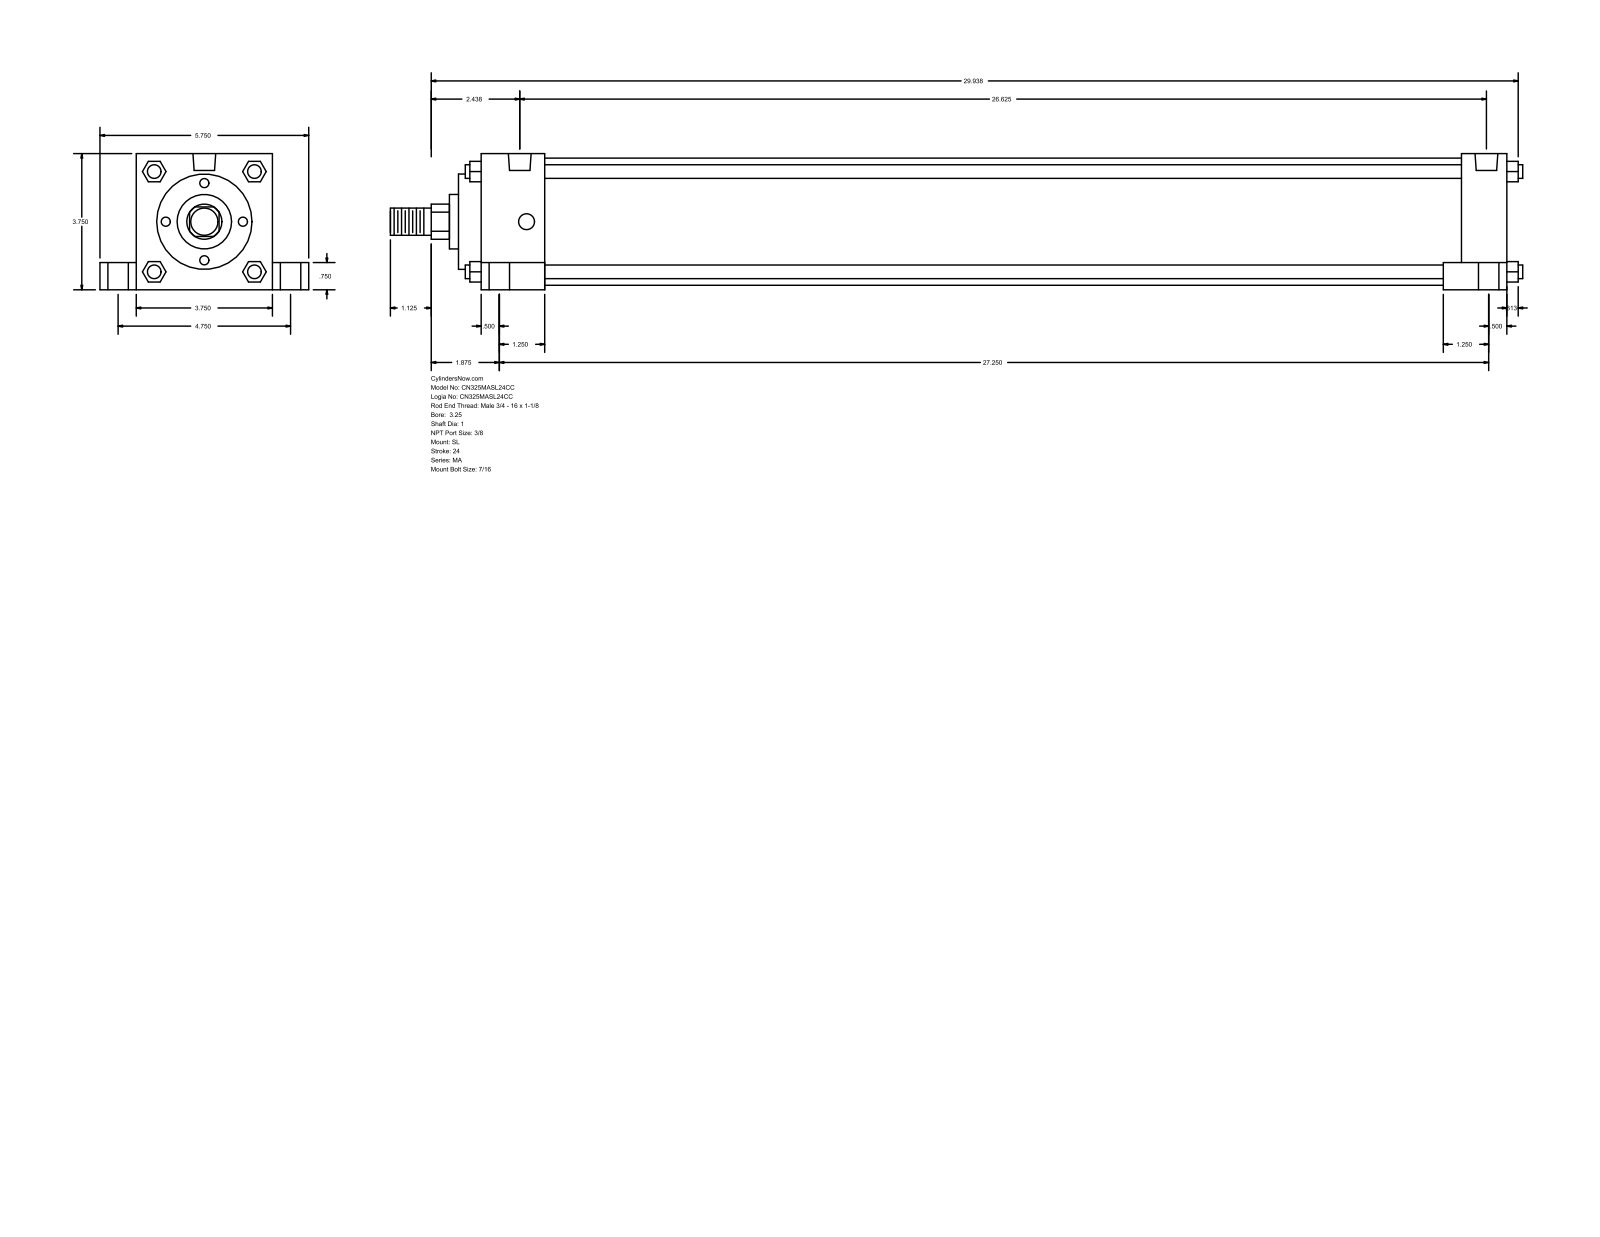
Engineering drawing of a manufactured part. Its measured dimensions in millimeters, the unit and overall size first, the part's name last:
Units: millimetres
Overall size (bounding box): 792.16 × 146.05 × 95.25
Round holes (diameter × count): ⌀11.11 ×4, ⌀14.29 ×4, ⌀20.64 ×4, ⌀15.93 ×2
Round bosses / shafts (diameter × count): ⌀9.53 ×4, ⌀88.9 ×1, ⌀66.67 ×1, ⌀38.1 ×1, ⌀25.4 ×1, ⌀19.05 ×1
Partial cylindrical surfaces — rounded edges, fillets, slot ends (radius × count): R12.29 ×1
Main face-to-face distances: 95.24, 717.56, 641.35, 15.87, 25.41, 120.65, 19.05, 685.81, 31.75, 44.46
Hole centre spacings: 60.35, 60.66, 62, 63.27, 120.66, 666.75, 675.8, 680.54
Bodies: 0 solids, 150 faces (113 planar, 37 cylindrical, 0 other)
Part name (STEP PRODUCT): MA_SL__0325_1
STEP written by: GSSL Pune (CONFIG_CONTROL_DESIGN)
